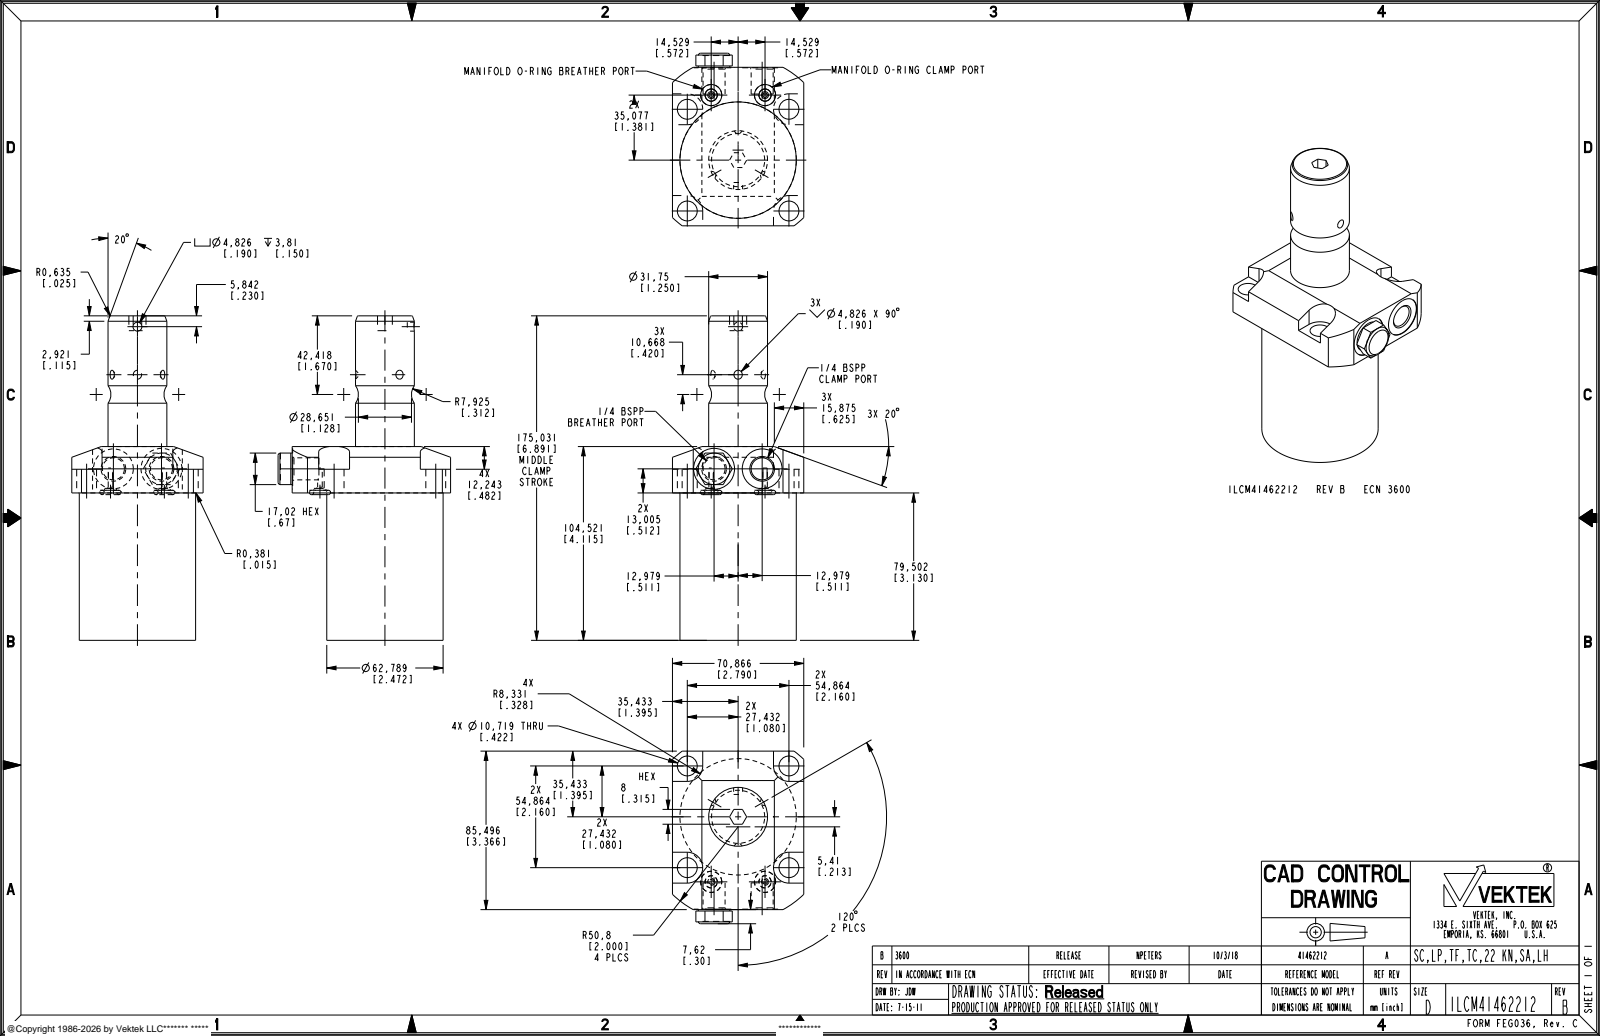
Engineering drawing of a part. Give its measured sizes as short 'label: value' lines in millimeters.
name: ILCM41462212
written by: PRO/ENGINEER BY PARAMETRIC TECHNOLOGY CORPORATION, 2013320 (AUTOMOTIVE_DESIGN)
unit: mm
bodies: 3 solids, 143 faces (63 planar, 48 cylindrical, 32 other)
size: 175.03 × 93.11 × 70.87
volume: 424 929 mm³; area: 45 234 mm²
holes: 4× ⌀10.72, 2× ⌀2.49, 2× ⌀6.5, 2× ⌀11.4, 2× ⌀11.89, 1× ⌀4.83, 1× ⌀17.02, 1× ⌀21.49, 1× ⌀22.1
bosses: 1× ⌀62.79, 1× ⌀31.75
rounds: 4× R8.33, 1× R50.8
face distances: 79.5, 104.52, 25.02, 70.86, 92.28, 12.78, 12.24, 175.03, 95.53, 82.75
hole spacings: 54.86, 15, 42.65, 63.83, 75.29, 77.58, 77.77, 25.96
